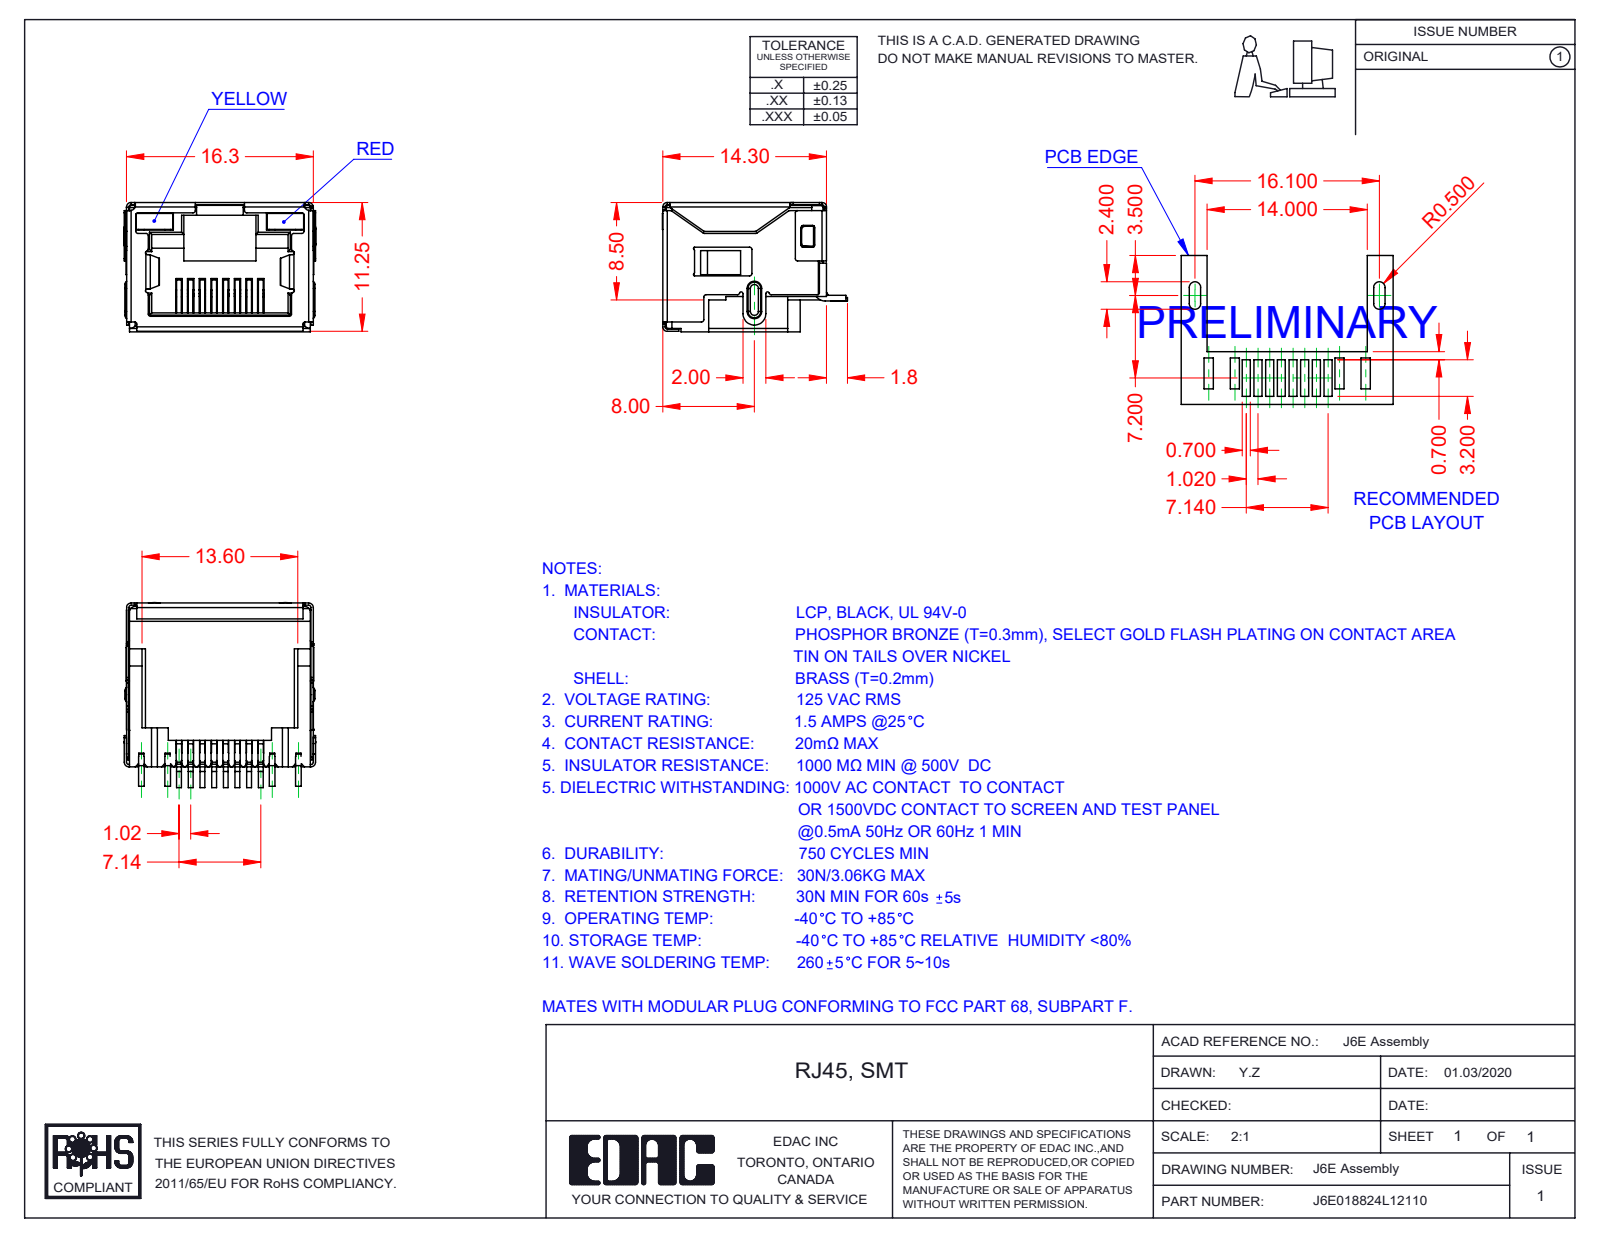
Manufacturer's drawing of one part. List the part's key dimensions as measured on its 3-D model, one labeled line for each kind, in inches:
Part name (STEP PRODUCT): 6E LED LH_1-Yellow; 6E Insulator_LED; J6E018824L12110; 6E LED RH_2-Red (+2 more)
STEP written by: SolidWorks 2016 (CONFIG_CONTROL_DESIGN)
Units: inches
Bodies: 12 solids, 1496 faces (1099 planar, 347 cylindrical, 50 other)
Overall size (bounding box): 0.659 × 0.636 × 0.445
Volume: 0.068 in³ · Surface area: 6.27 in²
Partial cylindrical surfaces — rounded edges, fillets, slot ends (radius × count): R0.008 ×82, R0.01 ×17, R0.016 ×13, R0.02 ×13, R0.004 ×10, R0.006 ×7, R0.012 ×4, R0.039 ×3
Main face-to-face distances: 0.435, 0.632, 0.634, 0.624, 0.437, 0.445, 0.094, 0.028, 0.388, 0.019
